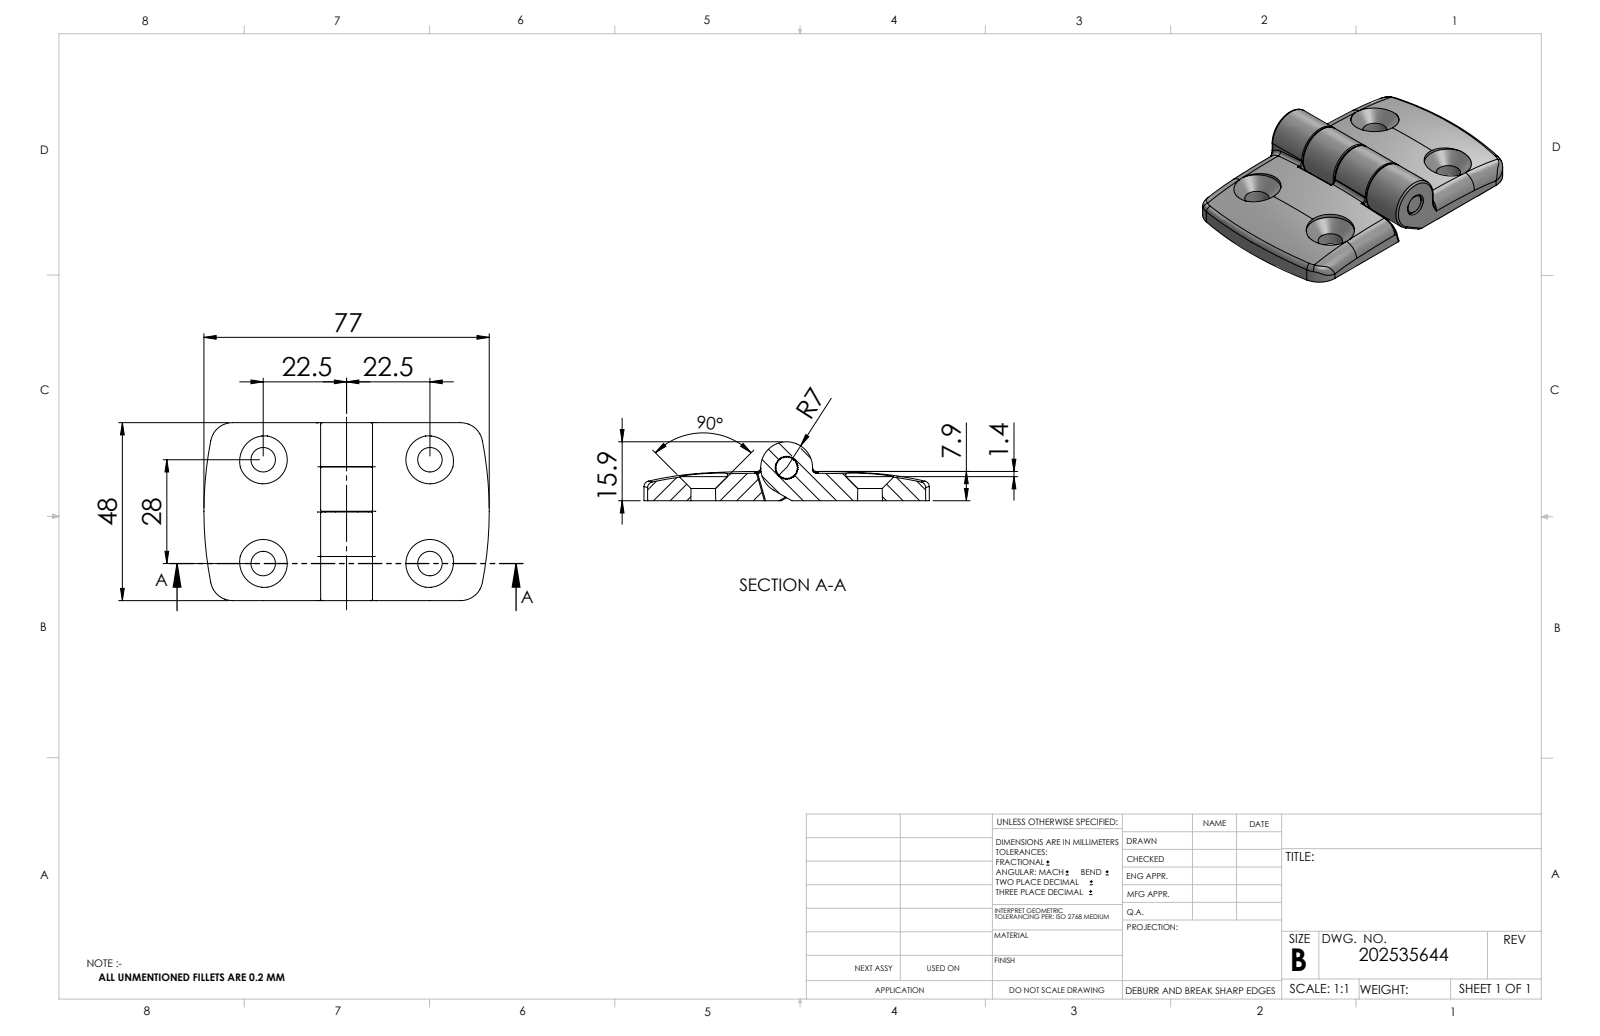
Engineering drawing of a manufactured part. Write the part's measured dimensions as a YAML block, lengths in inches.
part_name: "095a-02e_Standard; 095a40f_095A40F - 114345; 202535644_c_1"
step_written_by: "SolidWorks 2014 (CONFIG_CONTROL_DESIGN)"
units: inches
bodies: {solids: 3, faces: 477, planar: 208, cylindrical: 135, other: 134}
overall_size: [3.031, 1.89, 0.626]
volume: 1.513
surface_area: 19.88
round_holes:
  - {diameter: 0.236, count: 1}
round_bosses_or_shafts:
  - {diameter: 0.551, count: 1}
partial_cylinders:
  - {radius: 0.012, count: 22}
  - {radius: 0.008, count: 20}
  - {radius: 0.02, count: 12}
  - {radius: 0.236, count: 4}
  - {radius: 0.256, count: 4}
  - {radius: 3.937, count: 2}
  - {radius: 0.122, count: 1}
face_to_face_distances: [0.469, 1.421, 0.118, 0.48, 0.941, 0.949, 0.472, 0.953, 1.89, 0.158]
